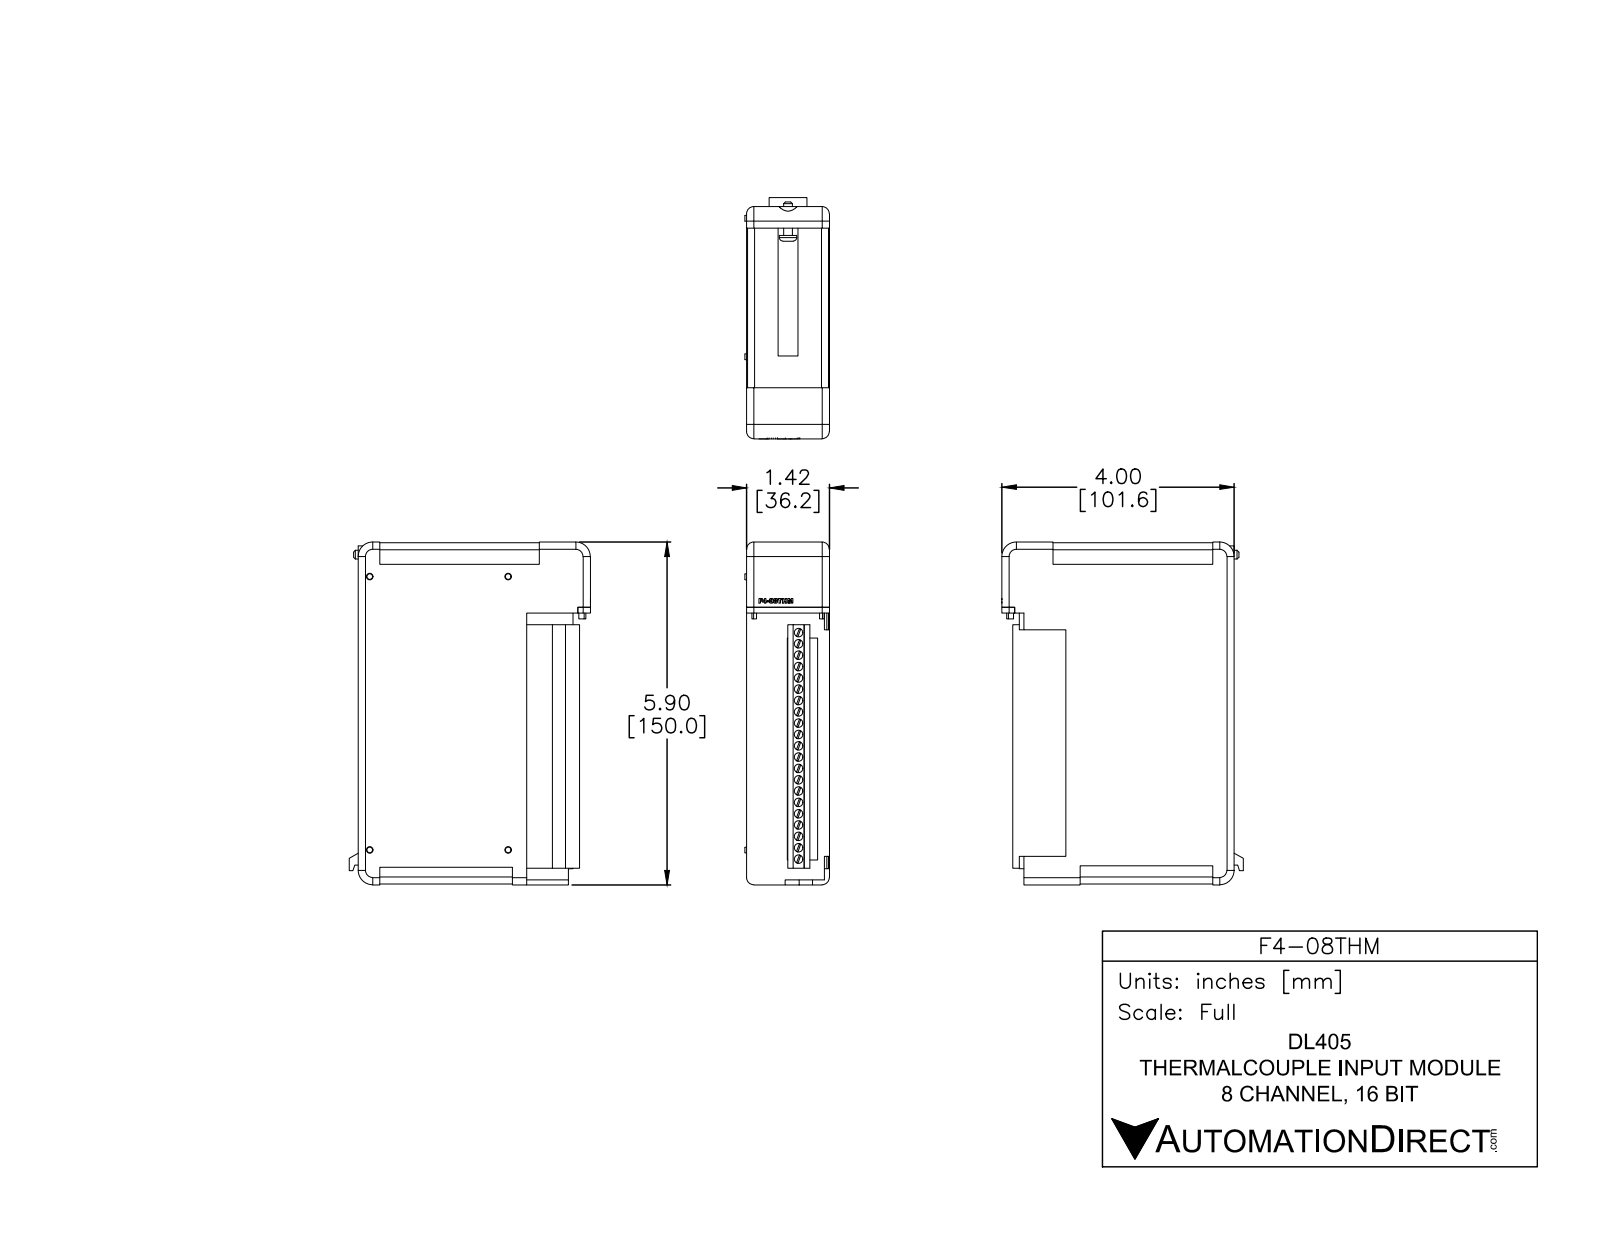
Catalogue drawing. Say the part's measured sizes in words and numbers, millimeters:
The part is named "F4-08THM". Its 3-D file was written by "SolidWorks 2014 (AUTOMOTIVE_DESIGN)". It is 11 solids with 450 faces: 325 planar, 77 cylindrical and 48 other. Overall it measures 150 by 105.6 by 37 millimeters. Its volume is 423 000 cubic millimeters and its surface area 66 000 square millimeters. Round holes: 21 of diameter 3.8. Round bosses or shafts: 1 of diameter 7.6, 1 of diameter 3.8. Partial cylindrical surfaces (rounded edges, fillets, slot ends): 8 of radius 3.2, 4 of radius 3, 3 of radius 6.4, 2 of radius 0.4, 2 of radius 0.8, 1 of radius 3.8, 1 of radius 4.3. The main face-to-face distances are 36.2, 8.5, 27.7, 21, 6.7, 15.2, 2.5, 17.8, 73.7, 0.4. The hole center spacings are 14.9, 5, 19.8, 34.7, 29.7, 9.9, 49.5, 9.9.
